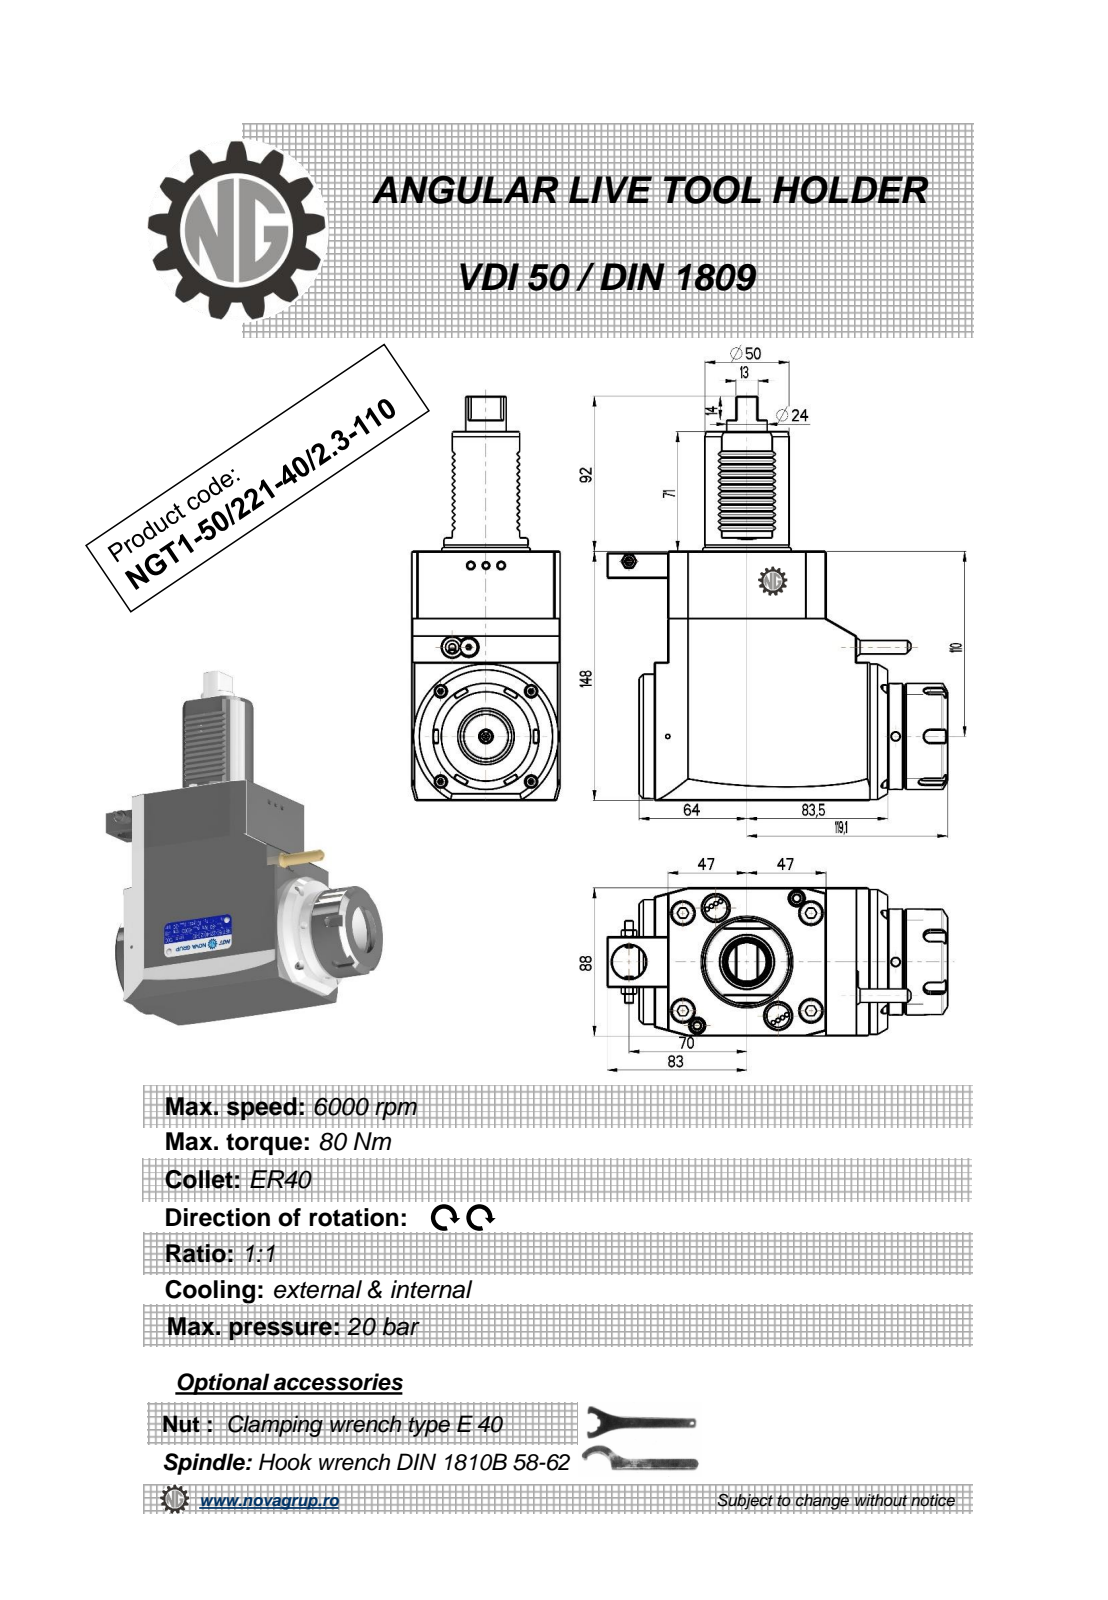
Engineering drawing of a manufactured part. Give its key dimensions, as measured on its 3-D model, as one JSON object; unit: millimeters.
{"part_name": "NGT1_50_221_40_1_3_110", "step_written_by": "PRO/ENGINEER BY PARAMETRIC TECHNOLOGY CORPORATION, 2010280 (CONFIG_CONTROL_DESIGN)", "units": "millimeters", "bodies": {"solids": 1, "faces": 468, "planar": 247, "cylindrical": 103, "other": 118}, "overall_size": [240, 202.1, 88], "volume_mm3": 1824000, "surface_area_mm2": 114980, "round_holes": [[5, 3], [3, 1], [9.5, 1], [20, 1], [33.5, 1]], "round_bosses_or_shafts": [[86, 1], [74, 1], [63, 1], [51, 1], [50, 1], [24, 1], [10, 1], [8.96, 1]], "partial_cylinders_radius": [[0.3, 24], [0.26, 12], [0.2, 6], [3.75, 5], [0.8, 2], [2.5, 1]], "face_to_face_distances": [88, 148, 147.5, 17, 8, 94, 111, 9, 130.5, 36.5], "hole_center_spacings": [52.46, 56.65, 101.5, 158.25]}
